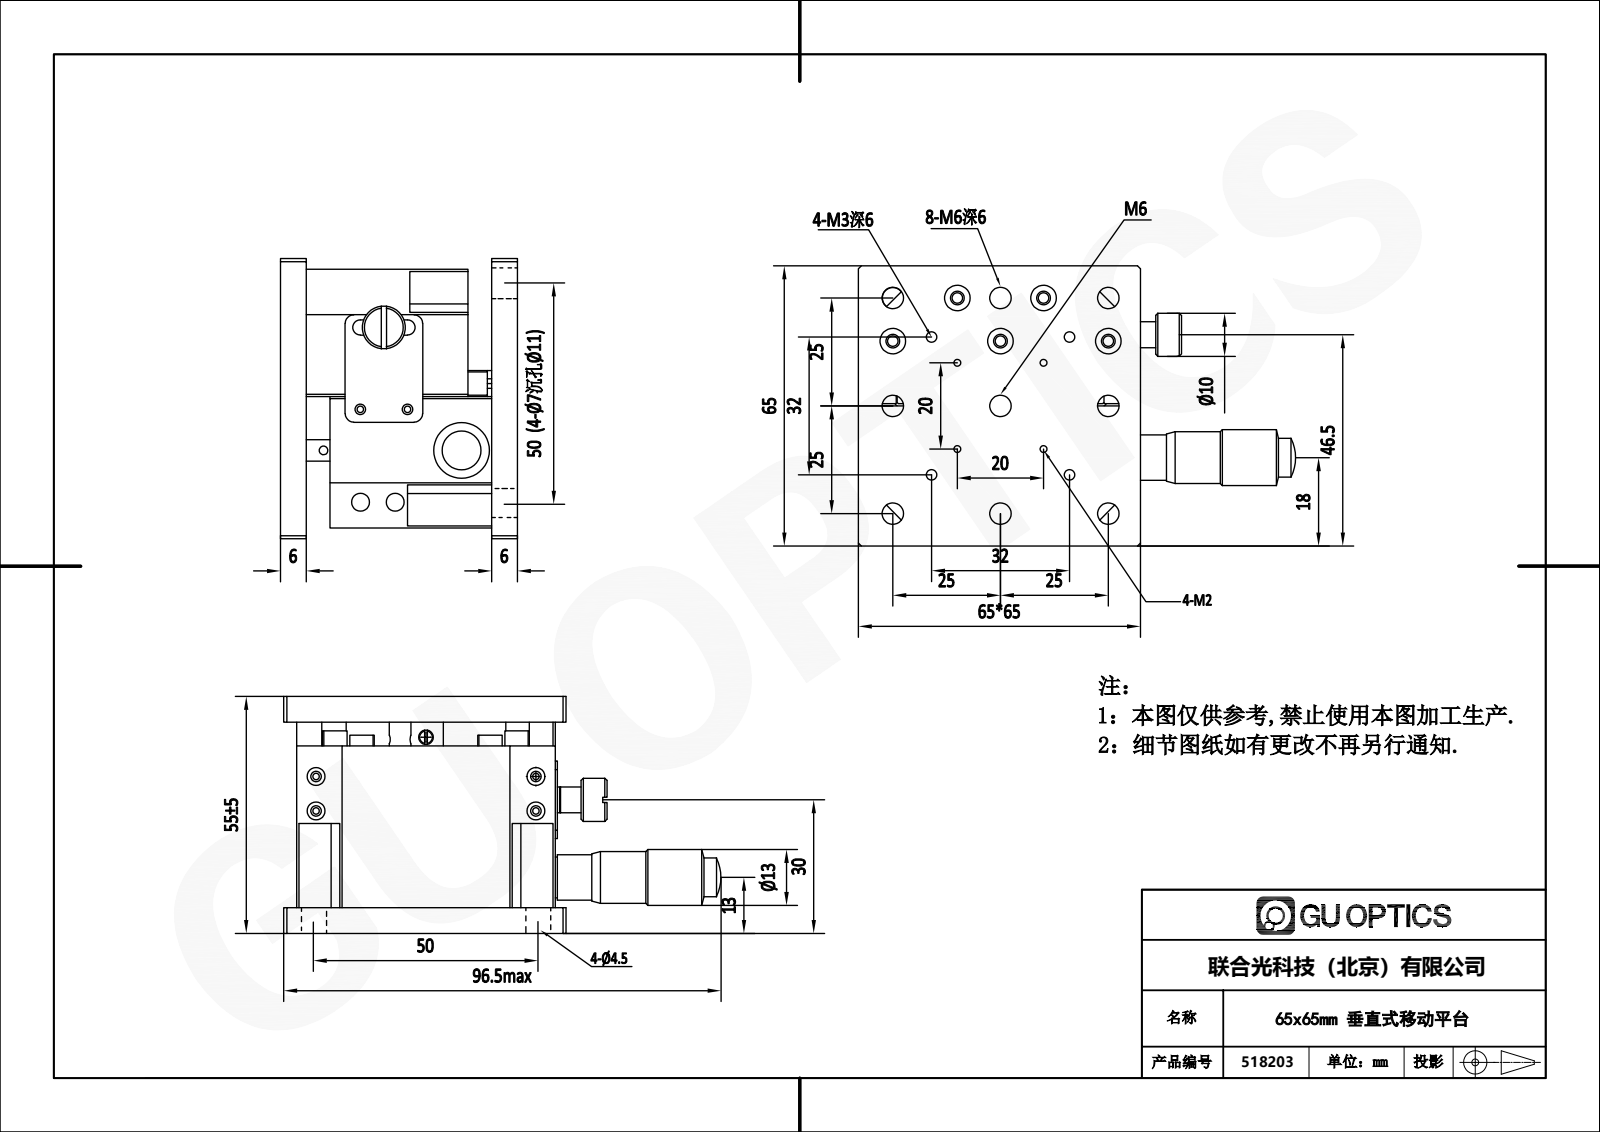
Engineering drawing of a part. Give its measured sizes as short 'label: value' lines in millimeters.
name: LZ65-2
written by: SolidWorks 2020 (CONFIG_CONTROL_DESIGN)
unit: mm
bodies: 5 solids, 441 faces (233 planar, 164 cylindrical, 44 other)
size: 101.5 × 65 × 55
volume: 154 727 mm³; area: 53 545 mm²
holes: 15× ⌀1.57, 14× ⌀2.46, 14× ⌀2.5, 12× ⌀3.2, 11× ⌀4, 11× ⌀6, 9× ⌀5, 4× ⌀1.6, 4× ⌀2.46, 4× ⌀4.2, 3× ⌀2.01, 3× ⌀7
bosses: 2× ⌀6, 2× ⌀5, 2× ⌀3.4, 2× ⌀2, 1× ⌀13, 1× ⌀12, 1× ⌀10.5, 1× ⌀10
rounds: 20× R0.5, 8× R2, 2× R1, 2× R1.75, 1× R3.5
face distances: 6, 49, 43, 2.5, 55, 11.5, 60, 30, 32.5, 10
hole spacings: 25, 20, 18.03, 35.36, 36.4, 15, 18.36, 26.68
